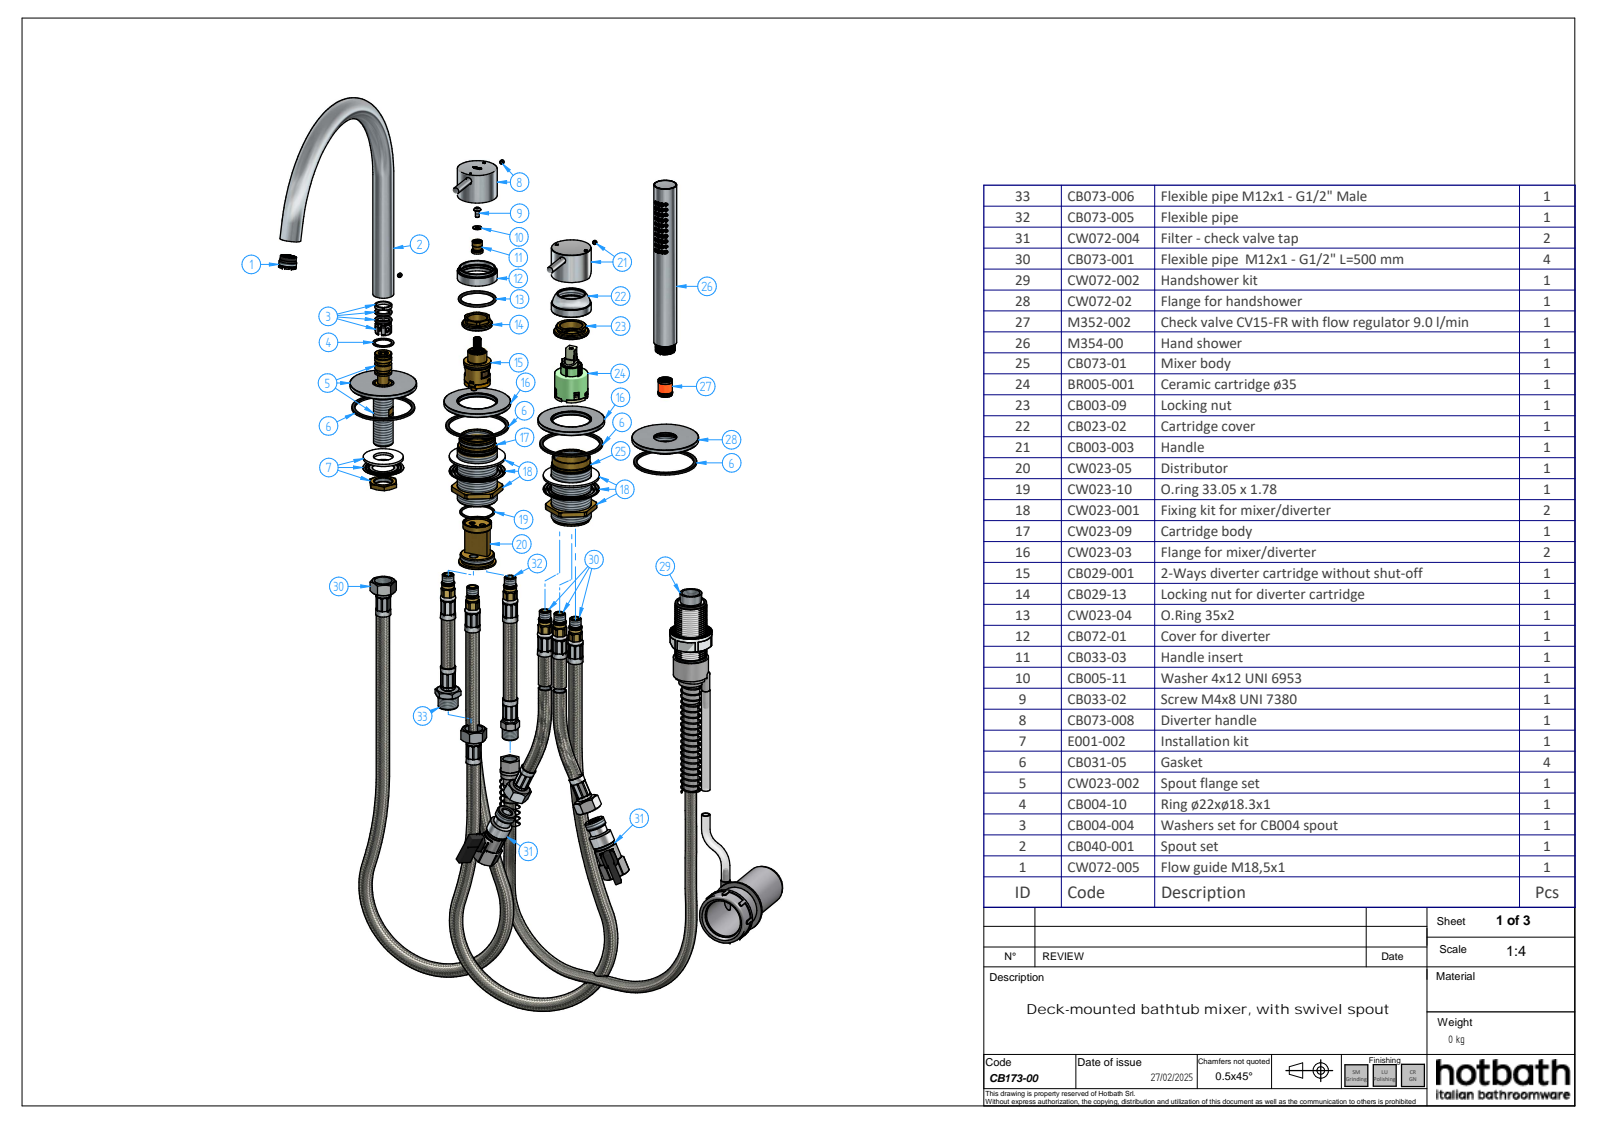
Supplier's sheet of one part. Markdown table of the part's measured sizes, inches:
| quantity | value |
| --- | --- |
| part name | CB173-00; CW023-03_oa_0; CW023-03_oa_1; CW023-002_oa_2 (+8 more) |
| STEP written by | Solid Edge (AP242_MANAGED_MODEL_BASED_3D_ENGINEERING_MIM_LF) |
| units | inches |
| bodies | 17 solids, 1140 faces (386 planar, 288 cylindrical, 466 other) |
| overall size | 15.748 × 10.505 × 10.457 |
| volume | 9.172 in³ |
| surface area | 256.8 in² |
| round holes (diameter × count) | 0.126 × 40, 0.197 × 4, 2.638 × 3, 0.13 × 2, 0.283 × 2, 0.709 × 2, 1.535 × 2, 1.572 × 2, 1.665 × 2, 0.157 × 1, 0.165 × 1, 0.394 × 1 |
| round bosses / shafts (diameter × count) | 2.756 × 4, 2.244 × 3, 1.693 × 2, 1.654 × 2, 0.866 × 2, 0.276 × 2, 1.102 × 1, 0.984 × 1 |
| partial cylindrical surfaces (radius × count) | 0.014 × 4, 0.197 × 4, 0.023 × 3, 0.03 × 3, 0.009 × 2, 0.009 × 2, 0.011 × 2, 0.017 × 2 |
| main face-to-face distances | 0.091, 0.067, 0.157, 0.02, 0.138, 0.047, 1.52, 1.677, 1.657, 1.61 |
| hole center spacings | 0.284, 0.236, 0.472, 0.498, 0.726, 0.157, 0.709, 0.958 |
